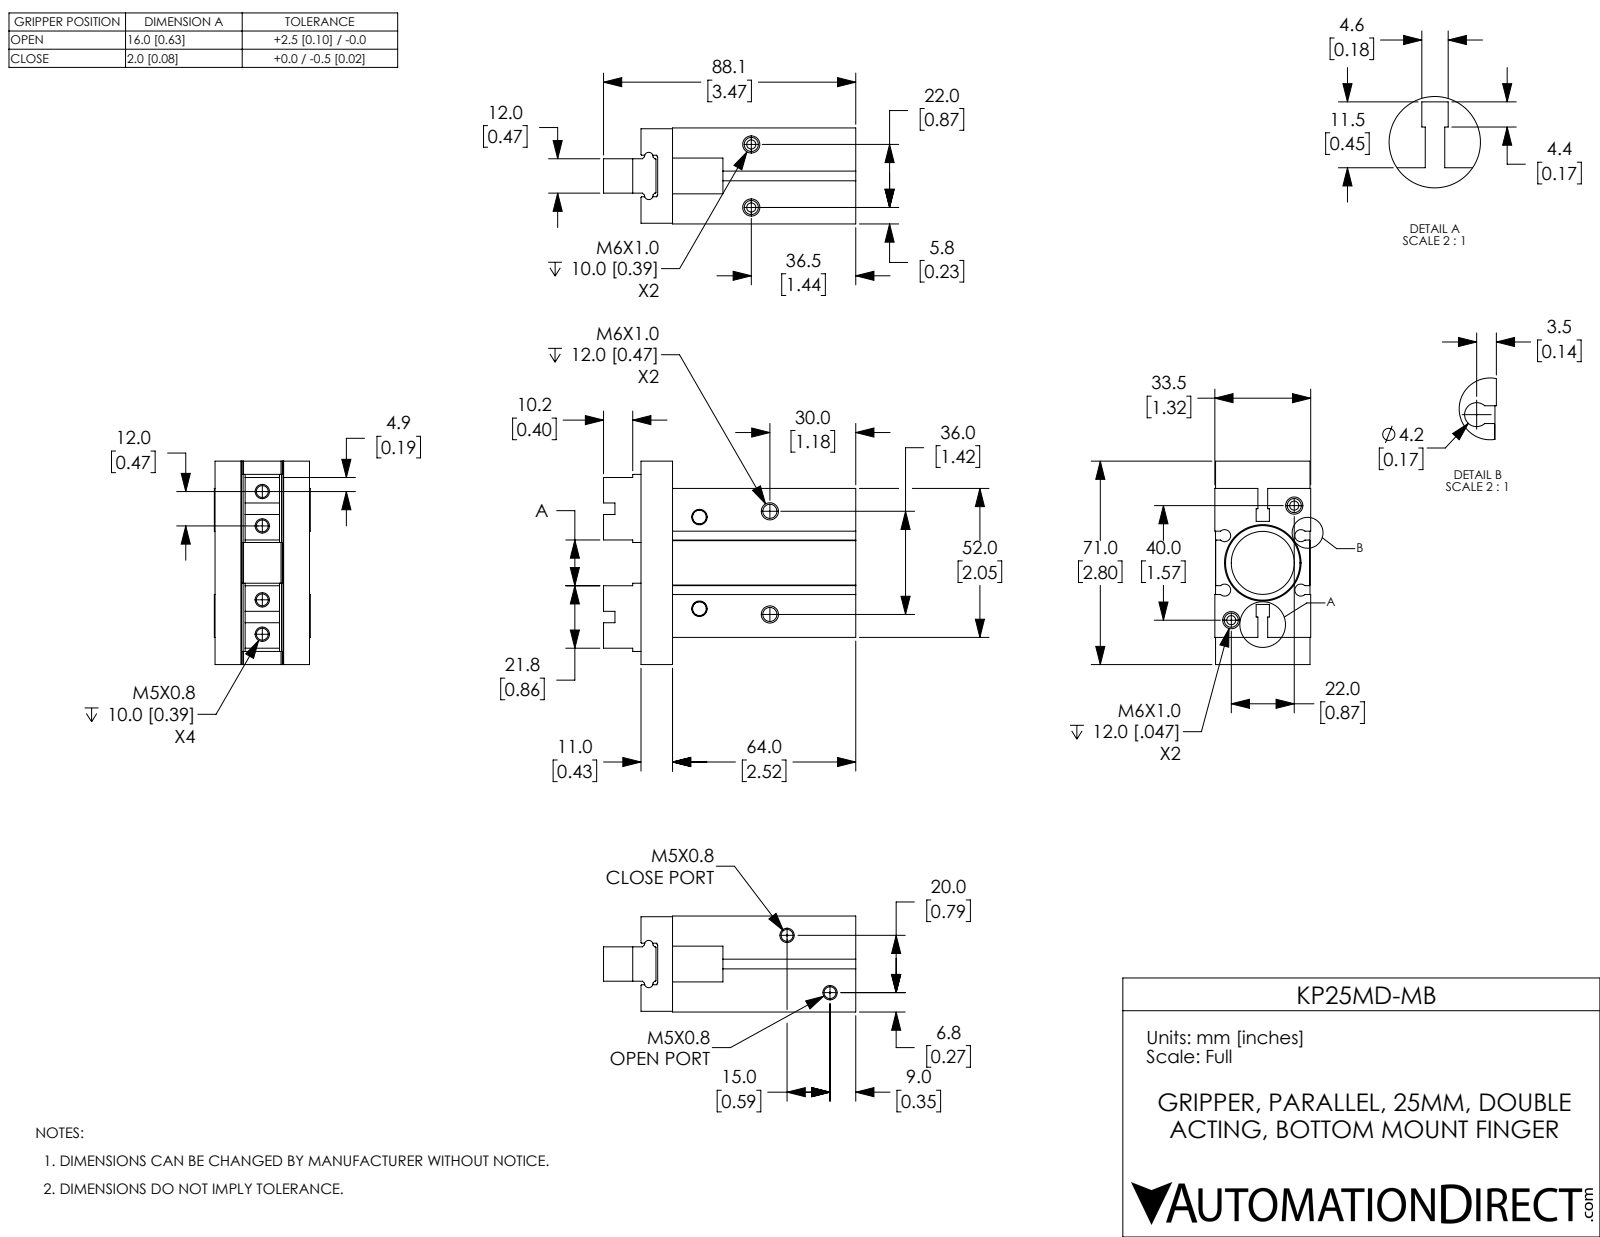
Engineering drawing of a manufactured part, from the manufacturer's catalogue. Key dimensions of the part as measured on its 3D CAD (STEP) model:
Part name (STEP PRODUCT): KP25MD-MB; KP25MD-MB-3; KP25MD-MB-2; KP25MD-MB-1
STEP written by: SolidWorks 2017 (CONFIG_CONTROL_DESIGN)
Units: millimetres
Bodies: 3 solids, 246 faces (128 planar, 64 cylindrical, 54 other)
Overall size (bounding box): 88.1 × 71 × 33.5
Volume: 115 673 mm³ · Surface area: 32 692 mm²
Round holes (diameter × count): ⌀4.13 ×6, ⌀4.92 ×4, ⌀0.5 ×2, ⌀4.92 ×2, ⌀6.02 ×2, ⌀22 ×1, ⌀26 ×1
Partial cylindrical surfaces — rounded edges, fillets, slot ends (radius × count): R0.2 ×8, R2.1 ×4, R0.5 ×2, R1.5 ×2
Main face-to-face distances: 10.5, 22.75, 33.2, 10.2, 23, 22.7, 33.5, 52, 33.25, 10.25
Hole centre spacings: 12, 12.04, 12.9, 13.09, 22.83, 24.9, 34.69, 37.8
